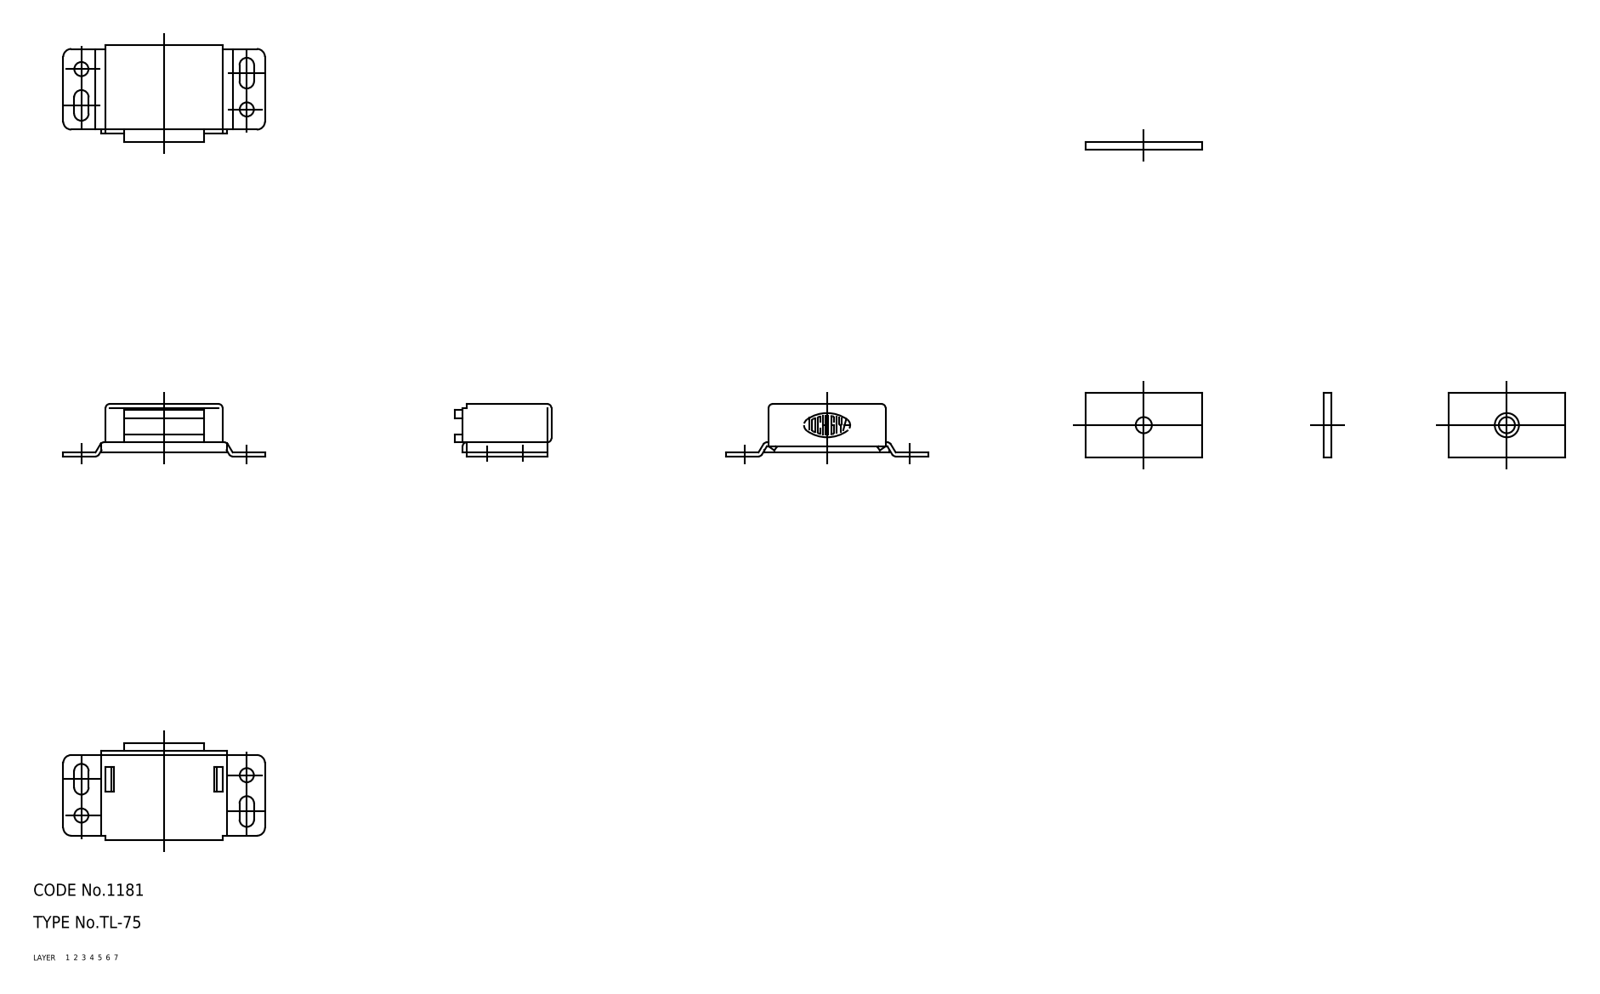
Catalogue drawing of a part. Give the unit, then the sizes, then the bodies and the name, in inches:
Units: inches
Overall size (bounding box): 1.969 × 1.85 × 0.63
Volume: 0.323 in³ · Surface area: 13.89 in²
Bodies: 5 solids, 122 faces (0 planar, 0 cylindrical, 122 other)
Part name (STEP PRODUCT): 67113322; 67113335; 67113348; 67113361 (+1 more)
STEP written by: CADfix (AUTOMOTIVE_DESIGN)
